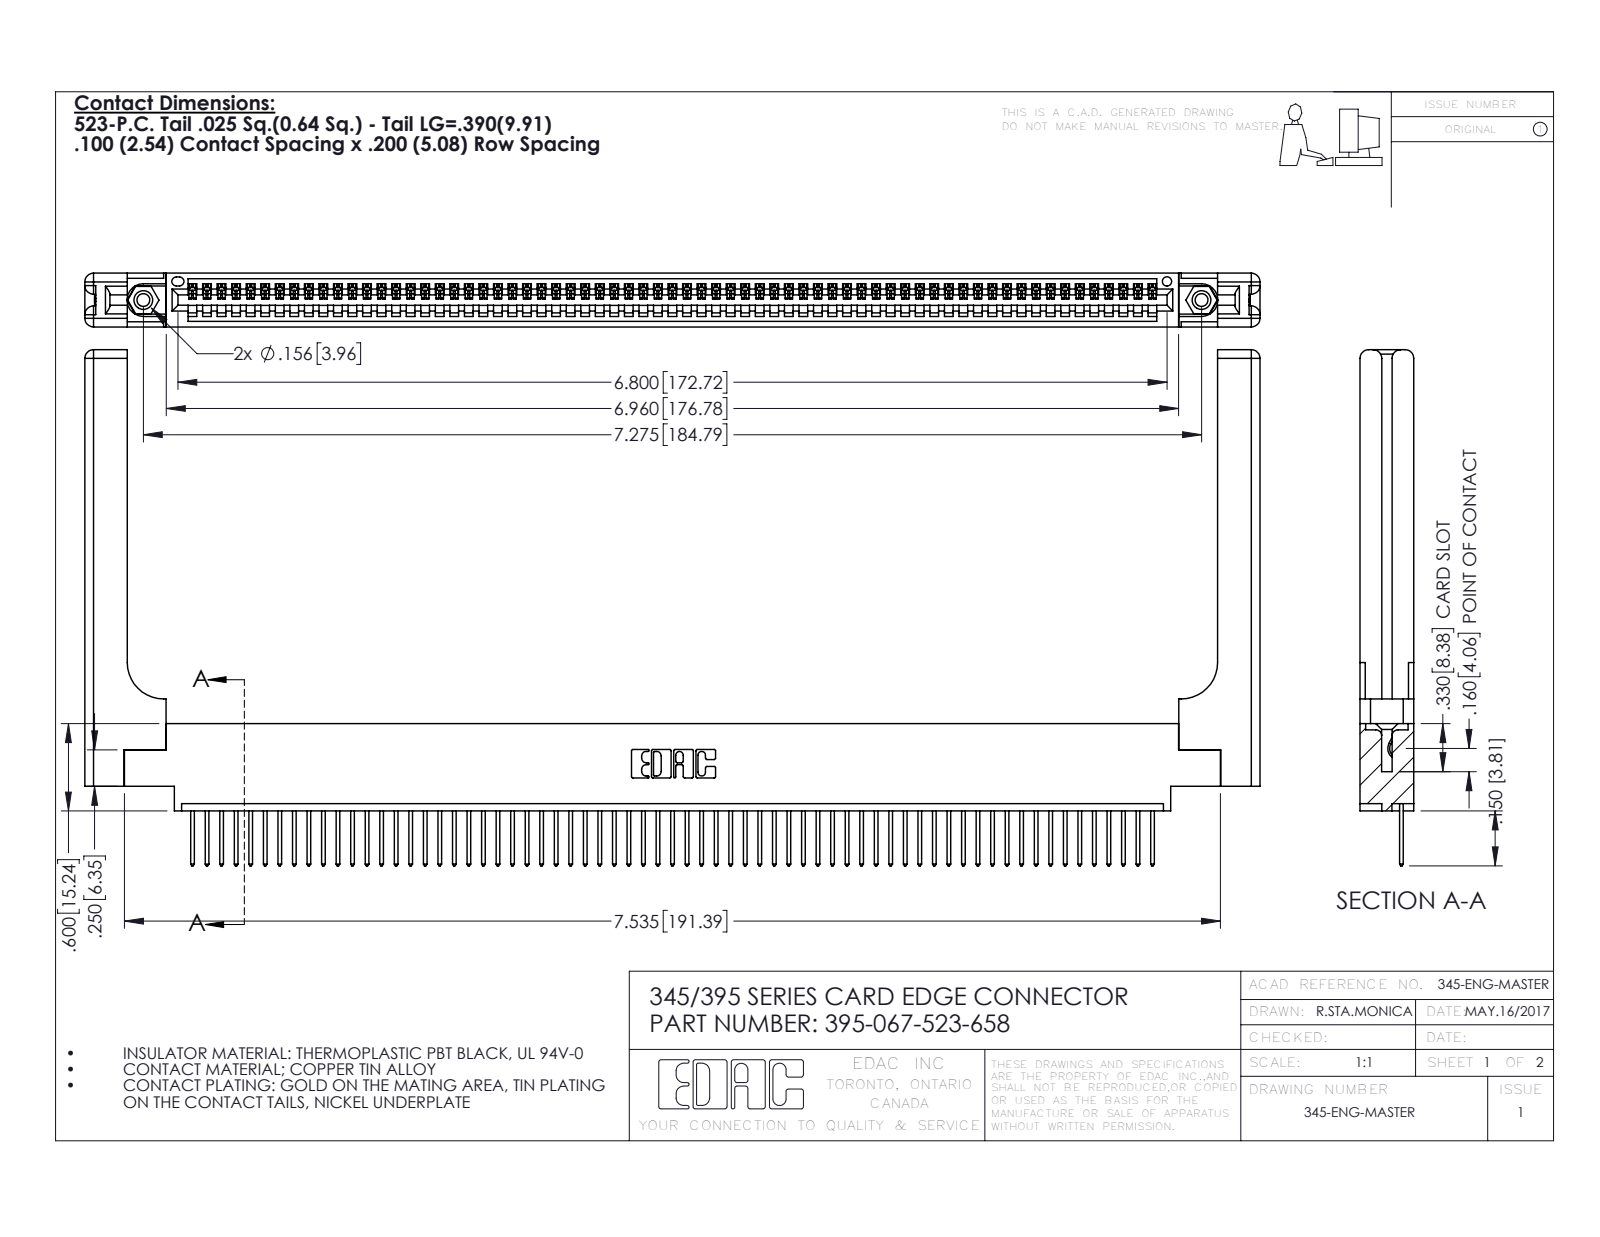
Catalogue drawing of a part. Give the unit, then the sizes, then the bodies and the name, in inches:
Units: inches
Overall size (bounding box): 8.079 × 3.547 × 0.37
Round holes (diameter × count): ⌀0.089 ×2, ⌀0.125 ×2, ⌀0.156 ×2, ⌀0.064 ×1
Round bosses / shafts (diameter × count): ⌀0.155 ×2
Partial cylindrical surfaces — rounded edges, fillets, slot ends (radius × count): R0.006 ×134, R0.01 ×134, R0.01 ×22, R0.06 ×16, R0.007 ×6, R0.031 ×6, R0.026 ×3, R0.03 ×2
Main face-to-face distances: 0.072, 0.298, 0.37, 0.098, 0.272, 0.025, 0.2, 0.225, 0.148, 0.15
Hole centre spacings: 0.27, 7.039, 7.275
Volume: 1.712 in³ · Surface area: 49.34 in²
Bodies: 72 solids, 4272 faces (2912 planar, 1300 cylindrical, 60 other)
Part name (STEP PRODUCT): 345-250-001_345-250-001-102; 395-067-523-658; 345-292-001_345-293-123; 345-220-058_345-220-058 (+1 more)
STEP written by: SolidWorks 2016 (CONFIG_CONTROL_DESIGN)
